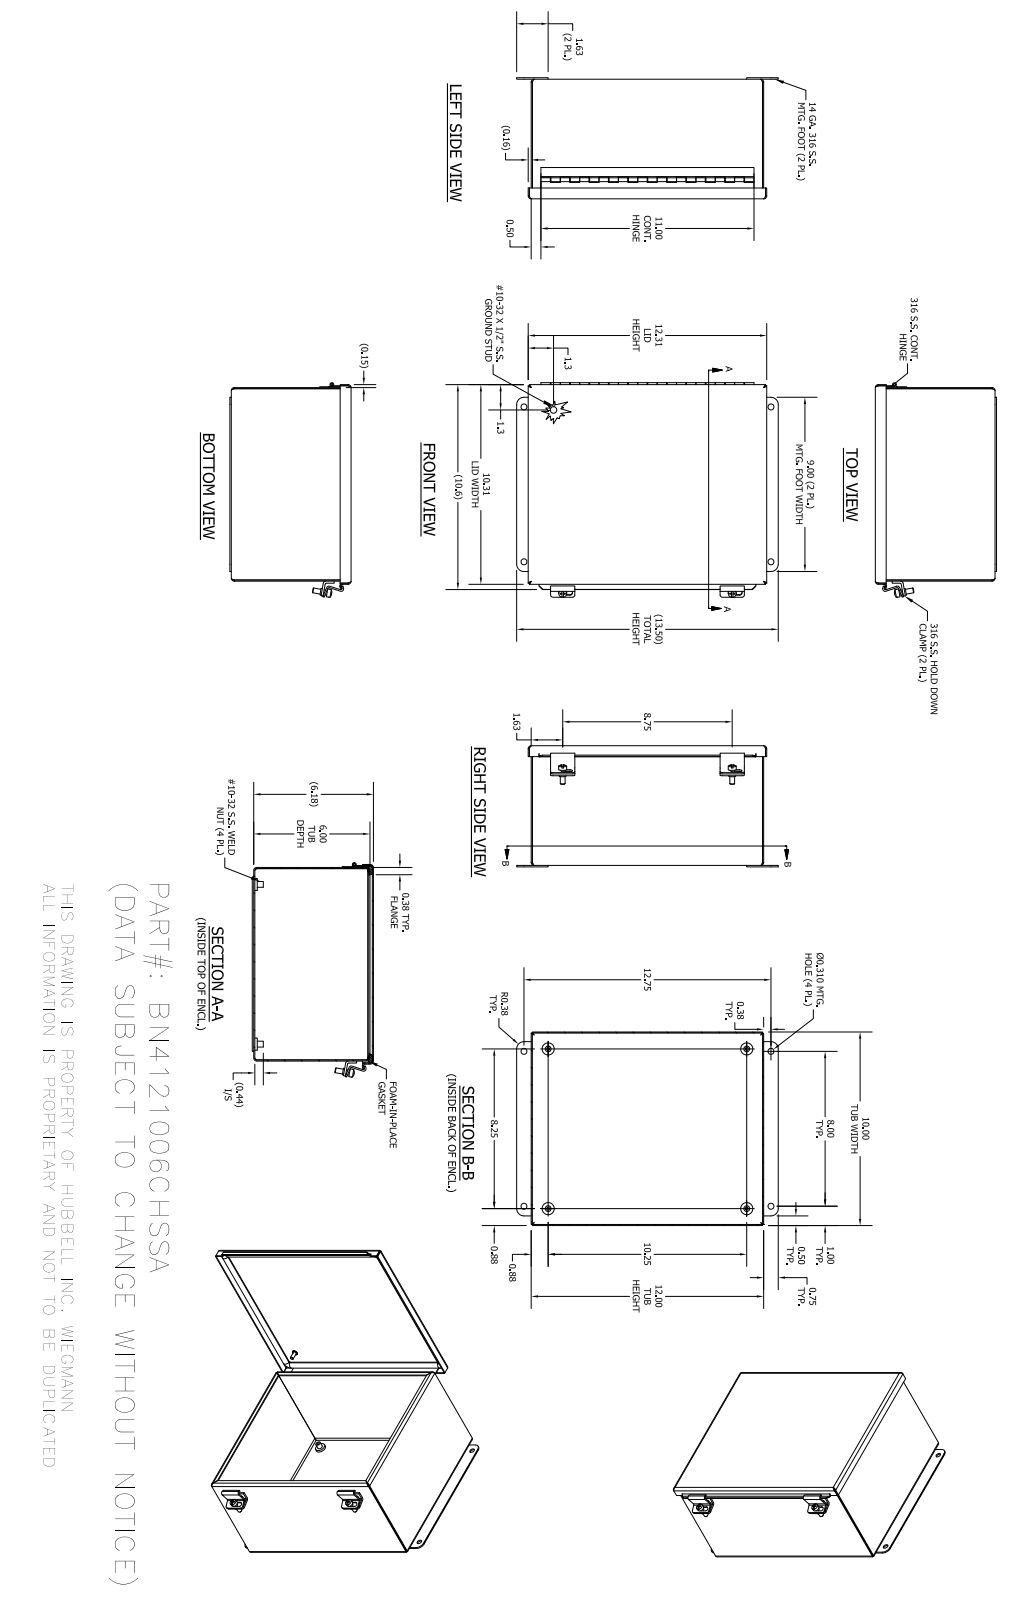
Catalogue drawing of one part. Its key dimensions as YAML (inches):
part_name: "B_121006_SSABKP; 32884LH; 32884P; 32884TH (+8 more)"
step_written_by: "Autodesk Inventor 2016 (AUTOMOTIVE_DESIGN)"
units: inches
bodies: {solids: 19, faces: 468, planar: 256, cylindrical: 145, other: 67}
overall_size: [13.5, 11.086, 6.256]
volume: 39.28
surface_area: 1260
round_holes:
  - {diameter: 0.11, count: 4}
  - {diameter: 0.156, count: 4}
  - {diameter: 0.31, count: 4}
  - {diameter: 0.196, count: 2}
  - {diameter: 0.117, count: 1}
round_bosses_or_shafts:
  - {diameter: 0.625, count: 4}
  - {diameter: 0.3, count: 4}
  - {diameter: 0.409, count: 2}
  - {diameter: 0.344, count: 2}
  - {diameter: 0.25, count: 2}
  - {diameter: 0.337, count: 1}
  - {diameter: 0.2, count: 1}
  - {diameter: 0.19, count: 1}
partial_cylinders:
  - {radius: 0.094, count: 13}
  - {radius: 0.153, count: 13}
  - {radius: 0.066, count: 8}
  - {radius: 0.125, count: 8}
  - {radius: 0.133, count: 4}
  - {radius: 0.228, count: 4}
  - {radius: 0.375, count: 4}
  - {radius: 0.063, count: 3}
face_to_face_distances: [0.059, 6.122, 9.941, 6.181, 6.063, 11.941, 10, 9.882, 12, 11.882]
hole_center_spacings: [1.256, 8, 8.75, 11.501, 14.081, 0.75, 8.22, 8.221]
